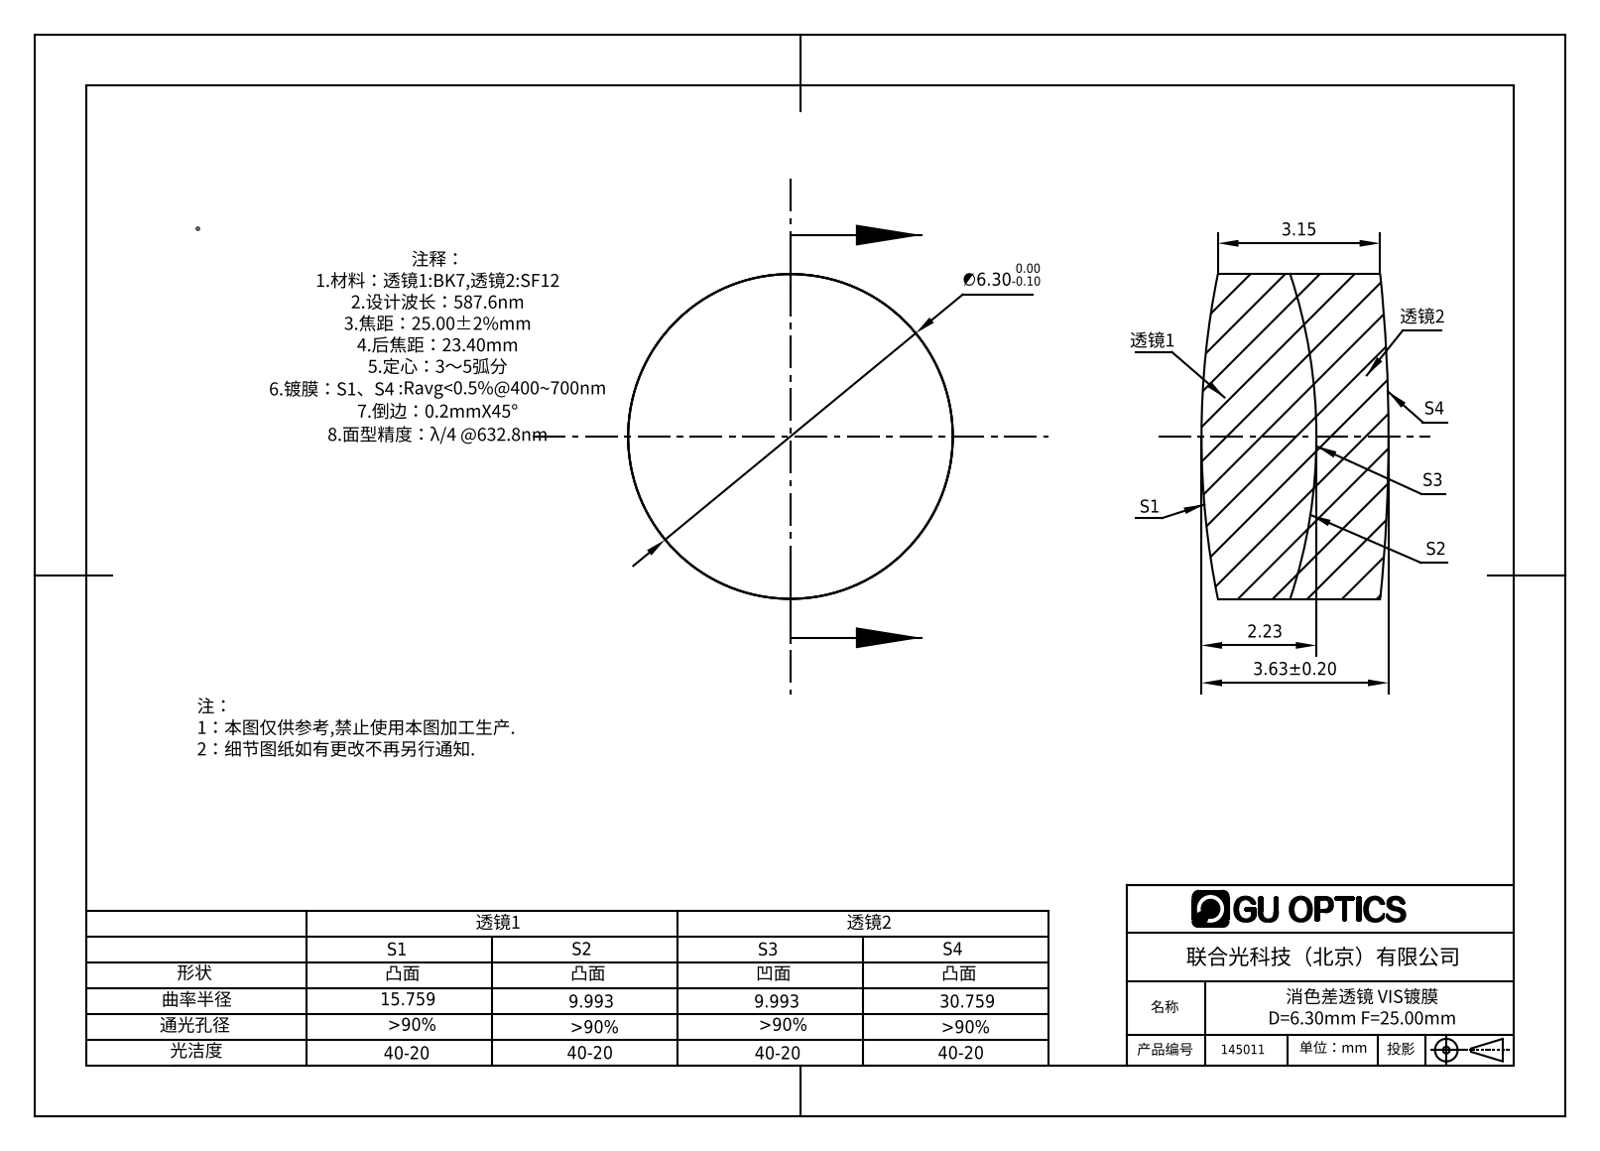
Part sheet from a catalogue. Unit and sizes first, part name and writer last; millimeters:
Units: millimetres
Overall size (bounding box): 6.3 × 6.3 × 3.63
Round bosses / shafts (diameter × count): ⌀6.3 ×1
Volume: 106 mm³ · Surface area: 189 mm²
Bodies: 2 solids, 12 faces (0 planar, 4 cylindrical, 8 other)
Part name (STEP PRODUCT): 145011
STEP written by: SolidWorks 2016 (AUTOMOTIVE_DESIGN)
